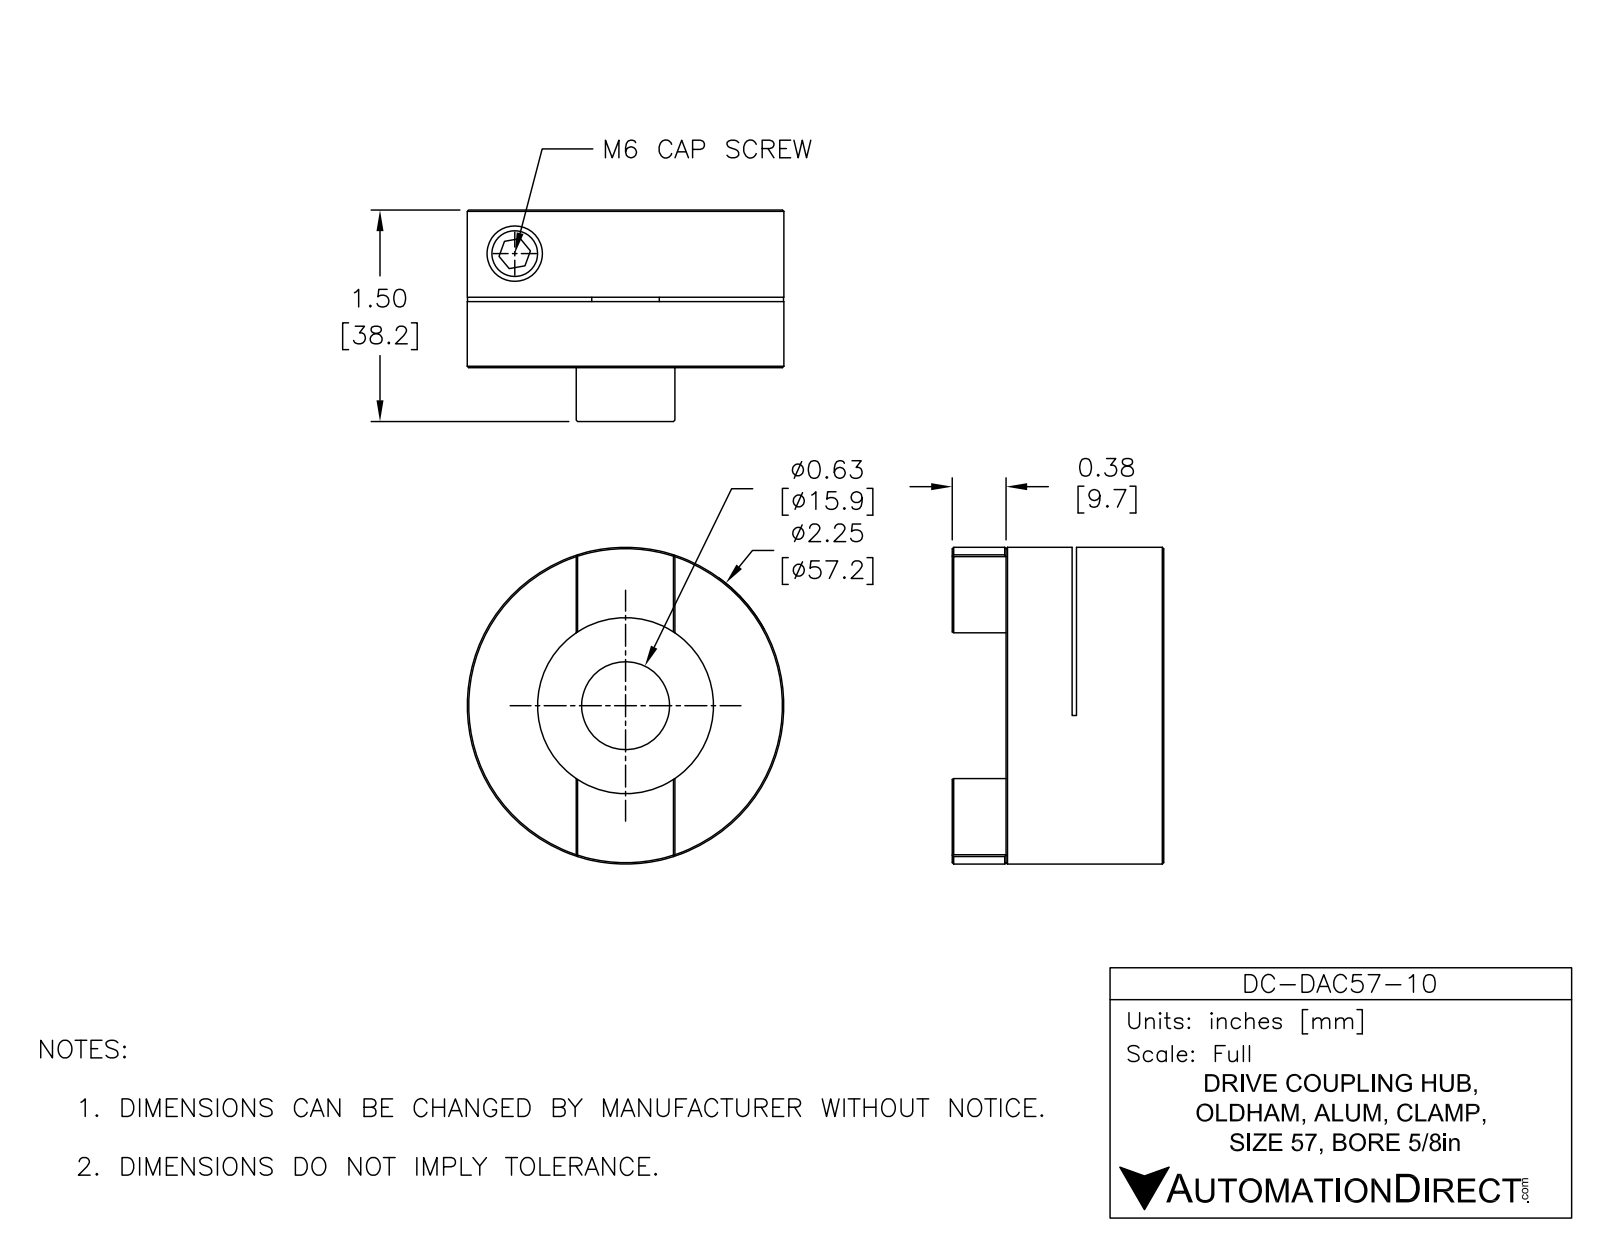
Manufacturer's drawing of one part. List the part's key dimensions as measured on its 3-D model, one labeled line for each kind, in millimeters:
Part name (STEP PRODUCT): DC-DAC57-10
STEP written by: SolidWorks 2015 (AUTOMOTIVE_DESIGN)
Units: millimetres
Bodies: 1 solid, 55 faces (29 planar, 16 cylindrical, 10 other)
Overall size (bounding box): 57.15 × 57.15 × 38.16
Volume: 70 201 mm³ · Surface area: 16 326 mm²
Round holes (diameter × count): ⌀4.93 ×1, ⌀6.6 ×1, ⌀11 ×1, ⌀12.7 ×1, ⌀31.75 ×1
Round bosses / shafts (diameter × count): ⌀57.15 ×1
Main face-to-face distances: 16.54, 28.45, 11.91, 15.75, 0.79, 12.7, 28, 12.25, 11.46, 0.45
